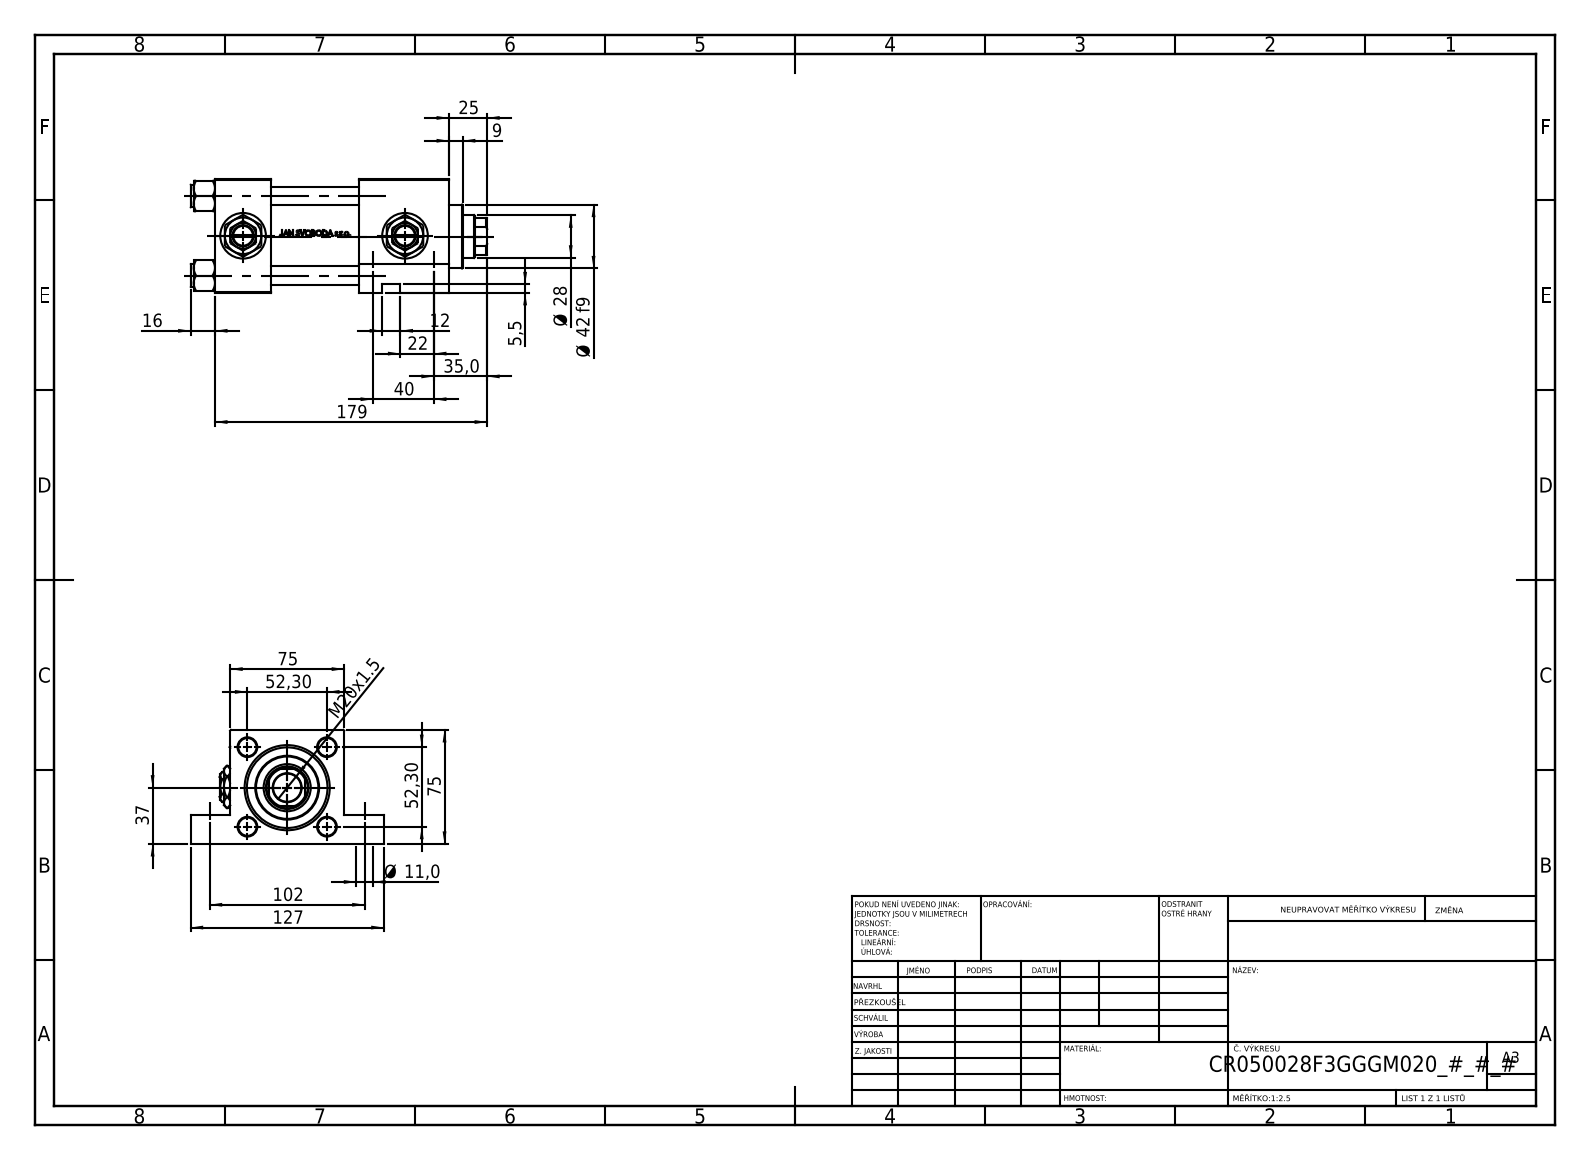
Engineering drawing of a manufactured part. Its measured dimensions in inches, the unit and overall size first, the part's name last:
Units: inches
Overall size (bounding box): 7.677 × 5 × 2.953
Round holes (diameter × count): ⌀0.472 ×4, ⌀0.825 ×4, ⌀1.181 ×4, ⌀0.276 ×3, ⌀0.433 ×2, ⌀0.433 ×2, ⌀0.728 ×1, ⌀1.102 ×1, ⌀1.22 ×1, ⌀1.614 ×1, ⌀1.969 ×1, ⌀2.087 ×1
Round bosses / shafts (diameter × count): ⌀0.591 ×4, ⌀2.205 ×1, ⌀1.654 ×1
Partial cylindrical surfaces — rounded edges, fillets, slot ends (radius × count): R0.531 ×1
Main face-to-face distances: 2.953, 1.457, 6.063, 4.606, 2.283, 3.74, 2.323, 0.748, 2.205, 2.945
Hole centre spacings: 2.059, 1.442, 1.47, 1.575, 2.032, 2.37, 2.912, 3.92
Volume: 43.51 in³ · Surface area: 254.8 in²
Bodies: 13 solids, 1202 faces (484 planar, 136 cylindrical, 582 other)
Part name (STEP PRODUCT): V215CR_VCP_F; V215_VC_A; NUT_M5_F; Zatka_pro_OIL_PORT (+2 more)
STEP written by: SolidWorks 2019 (CONFIG_CONTROL_DESIGN)
